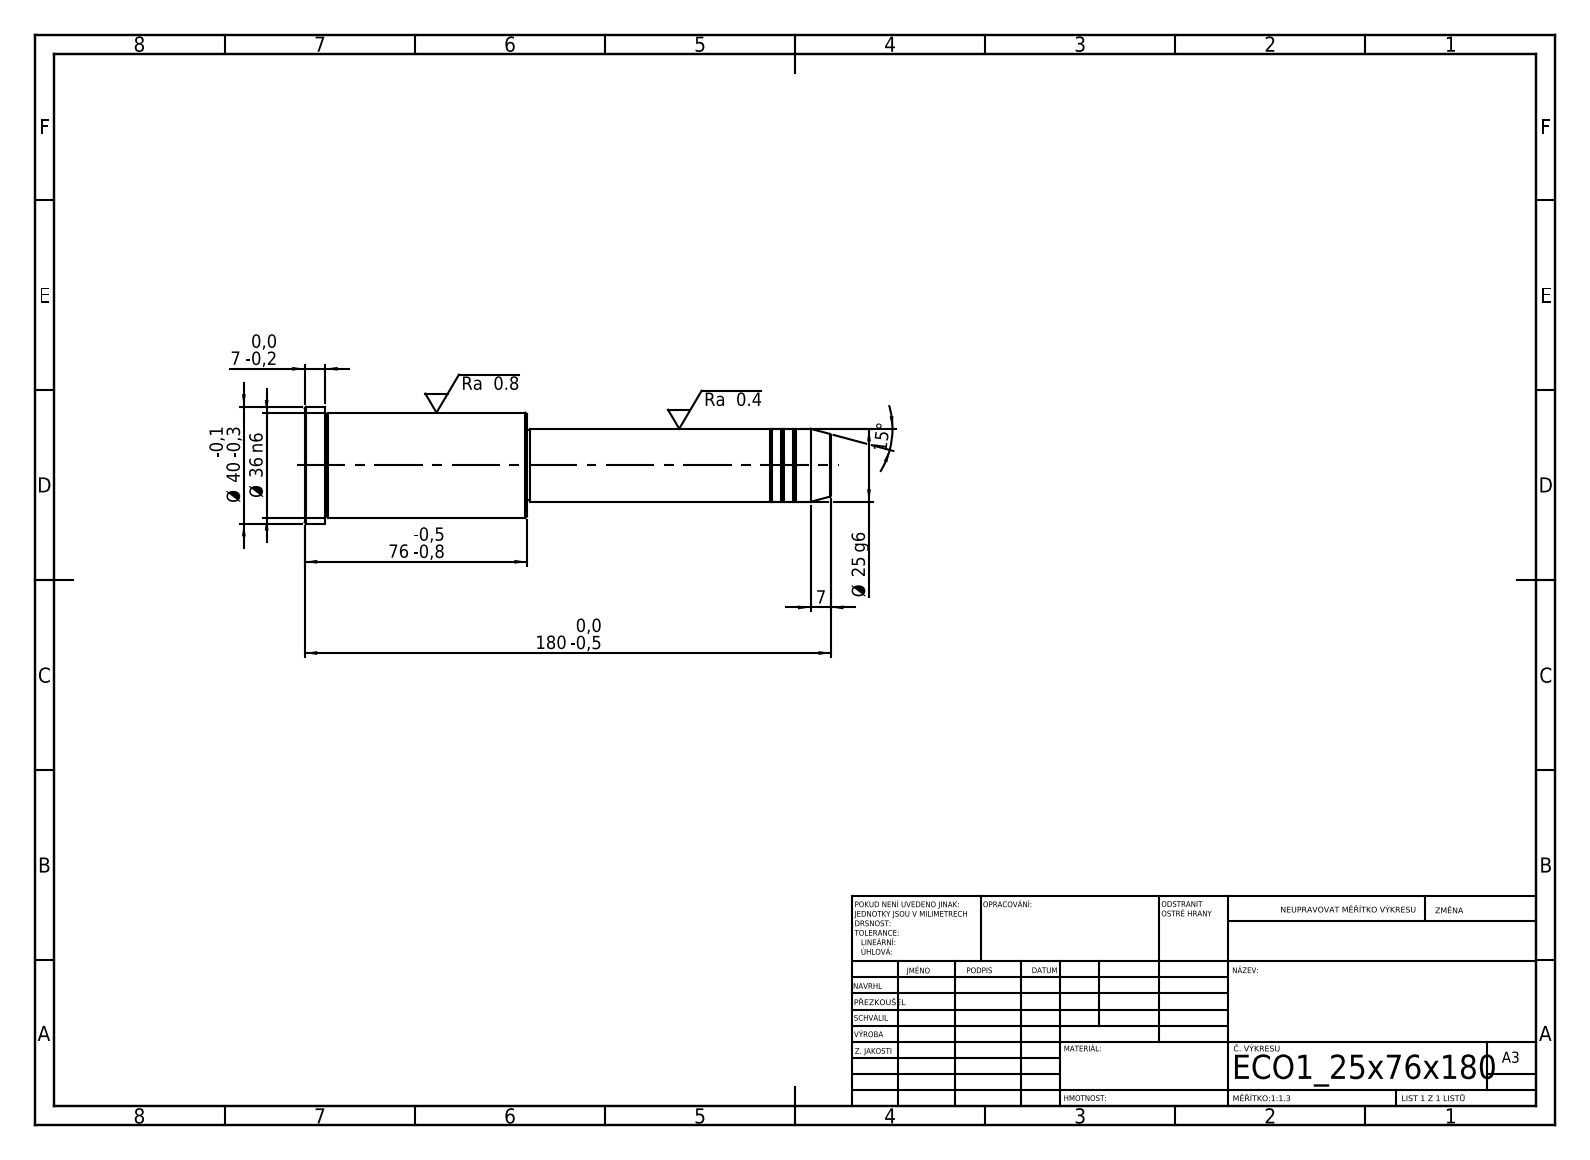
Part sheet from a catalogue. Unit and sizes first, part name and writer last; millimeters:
Units: millimetres
Overall size (bounding box): 180 × 40 × 40
Round bosses / shafts (diameter × count): ⌀40 ×1, ⌀36 ×1, ⌀25 ×1, ⌀24 ×1
Main face-to-face distances: 76, 104, 180, 173, 69, 7, 103, 1, 70, 77
Volume: 129 386 mm³ · Surface area: 19 387 mm²
Bodies: 1 solid, 43 faces (5 planar, 14 cylindrical, 24 other)
STEP written by: SolidWorks 2019 (CONFIG_CONTROL_DESIGN)
